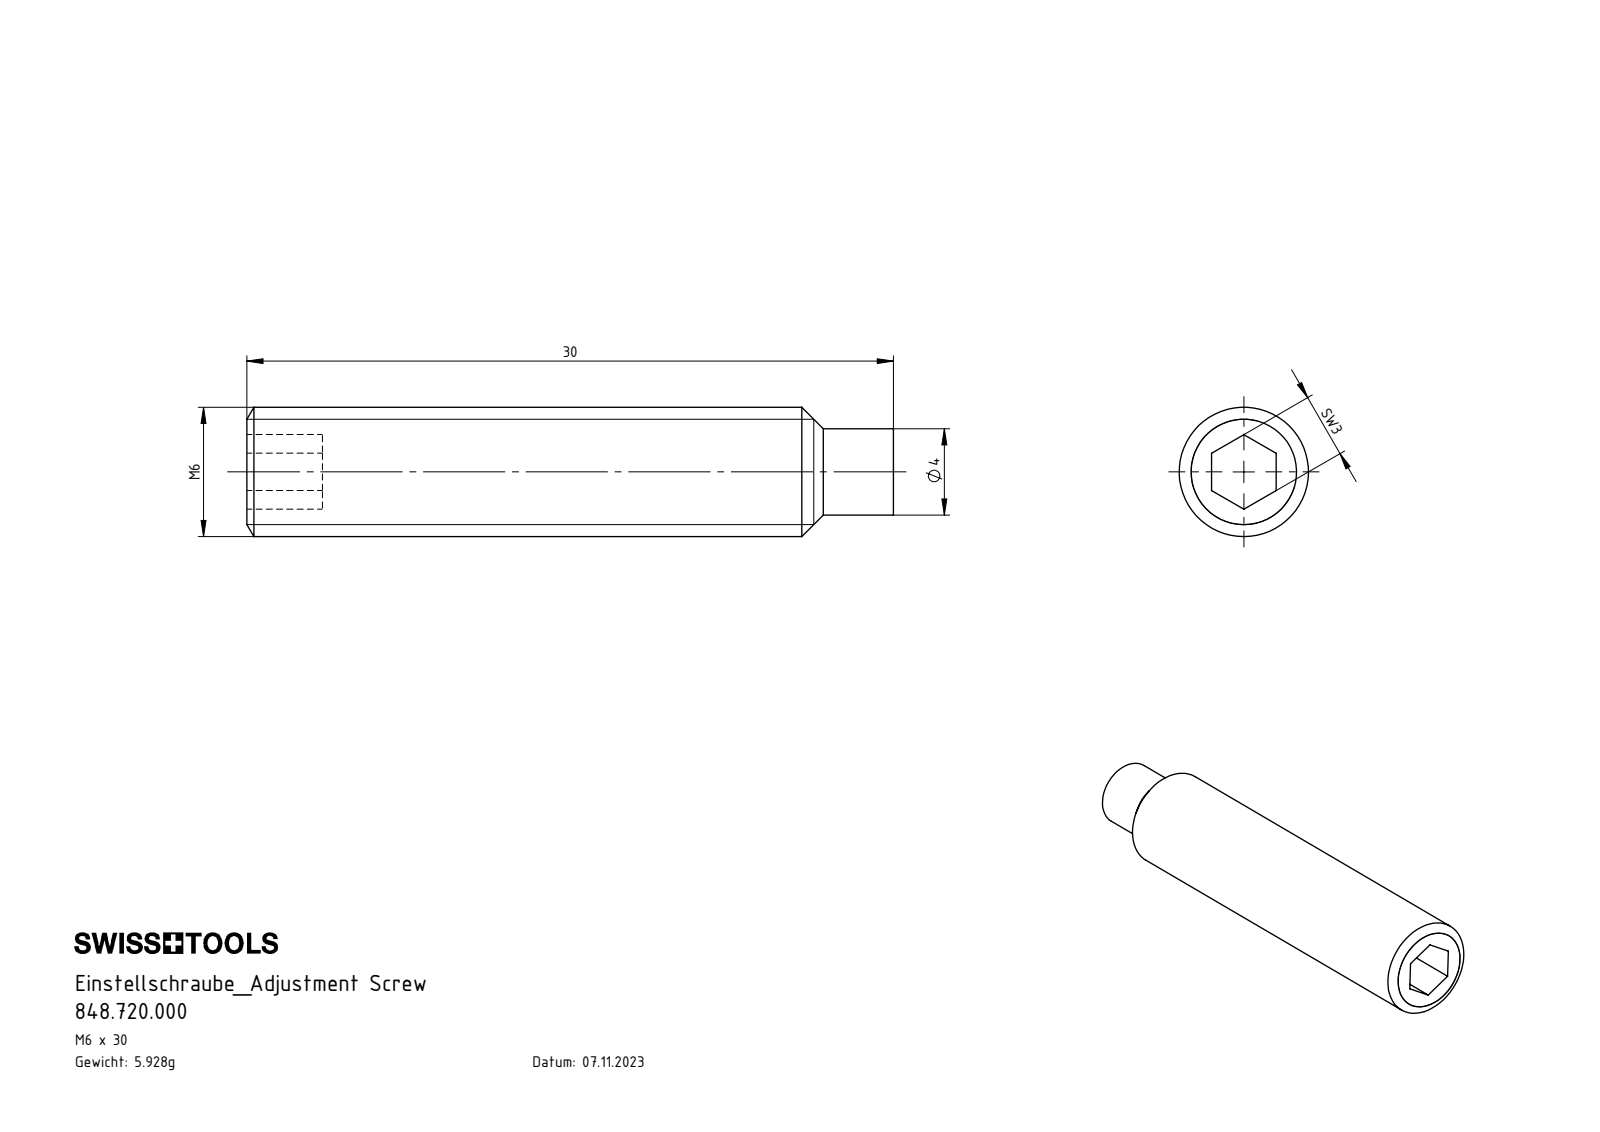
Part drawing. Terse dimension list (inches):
name: 848.720.000
written by: SolidWorks 2022 (AUTOMOTIVE_DESIGN)
unit: in
bodies: 1 solid, 17 faces (9 planar, 4 cylindrical, 4 other)
size: 1.181 × 0.236 × 0.236
volume: 0.046 in³; area: 0.963 in²
bosses: 1× ⌀0.236, 1× ⌀0.157
face distances: 0.118, 1.181, 0.138, 1.043
